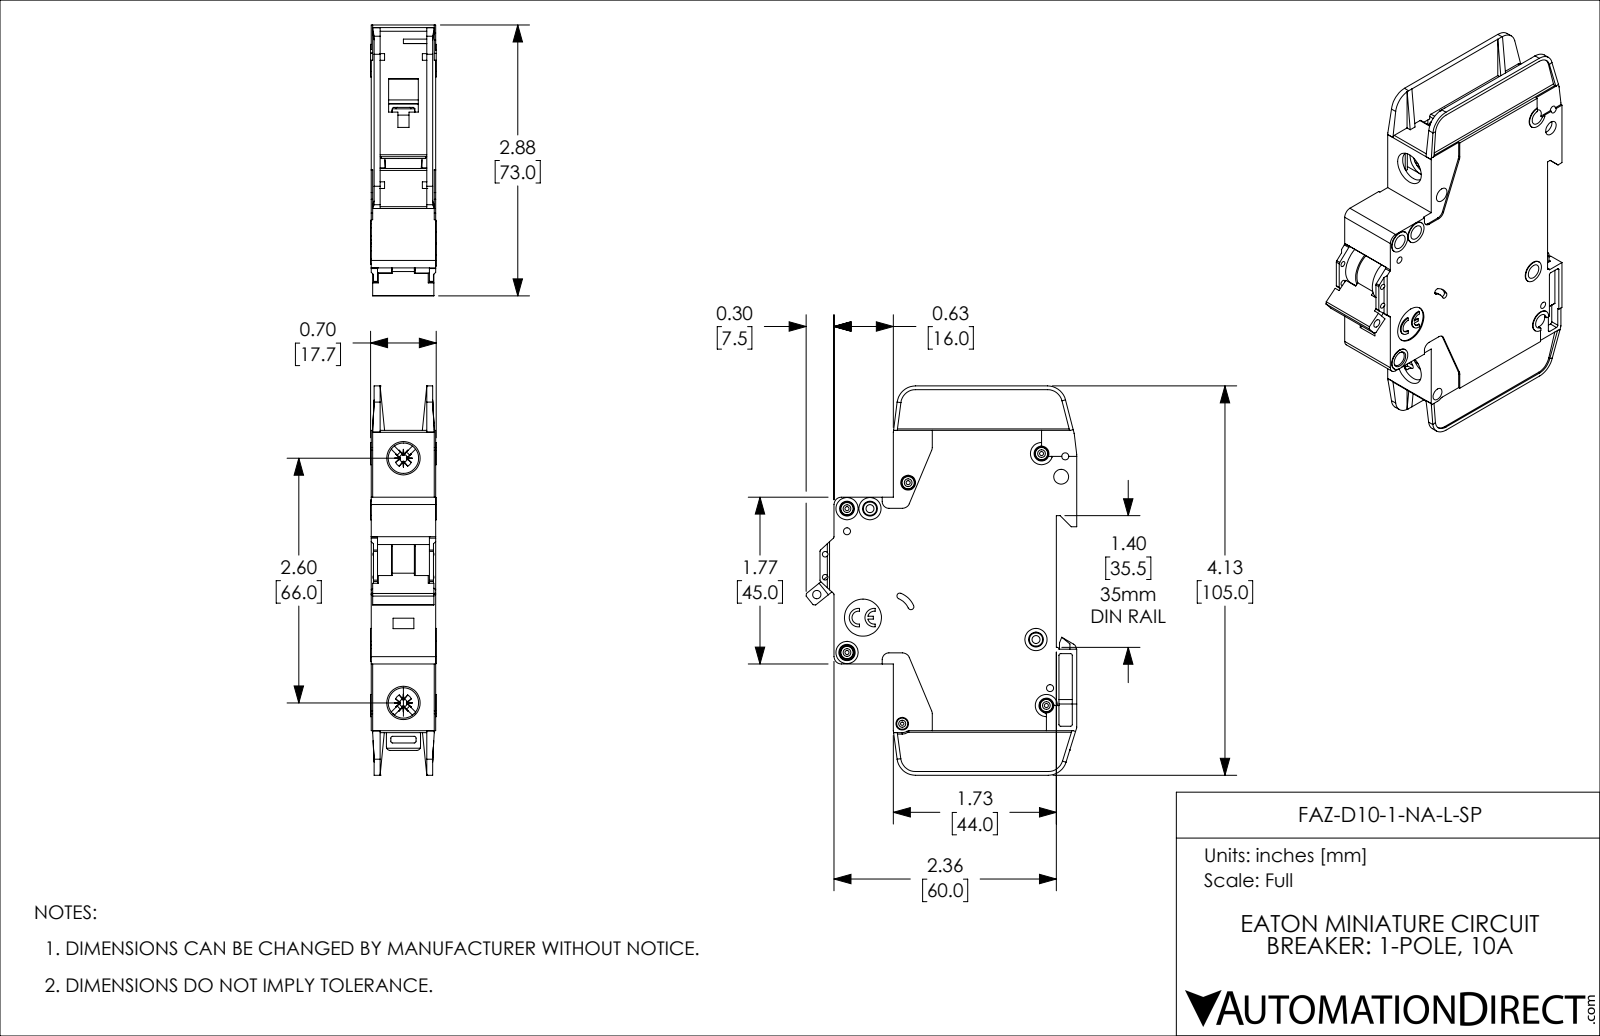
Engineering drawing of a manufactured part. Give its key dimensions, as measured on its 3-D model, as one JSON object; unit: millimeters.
{"part_name": "FAZ-D10-1-NA-L-SP", "step_written_by": "SolidWorks 2019 (AUTOMOTIVE_DESIGN)", "units": "millimeters", "bodies": {"solids": 1, "faces": 1127, "planar": 671, "cylindrical": 357, "other": 99}, "overall_size": [105, 73.1, 17.7], "volume_mm3": 76720, "surface_area_mm2": 26460, "round_holes": [[4, 8], [1.1, 5], [1.9, 4], [1.5, 2], [2.2, 2], [8.2, 2], [0.9, 1], [2.3, 1], [2.5, 1], [3.4, 1], [10, 1]], "round_bosses_or_shafts": [[3.3, 5], [6, 4], [3, 2], [2.5, 1]], "partial_cylinders_radius": [[0.5, 42], [0.4, 10], [1, 10], [2, 8], [5, 5], [0.2, 4], [0.7, 4], [1.1, 4]], "face_to_face_distances": [1.2, 17.4, 15, 16.2, 2.4, 13.8, 0.4, 0.8, 12.6, 14.6], "hole_center_spacings": [6.2, 13.6, 22.1, 4.8, 5.1, 5.2, 5.6, 6.1]}
